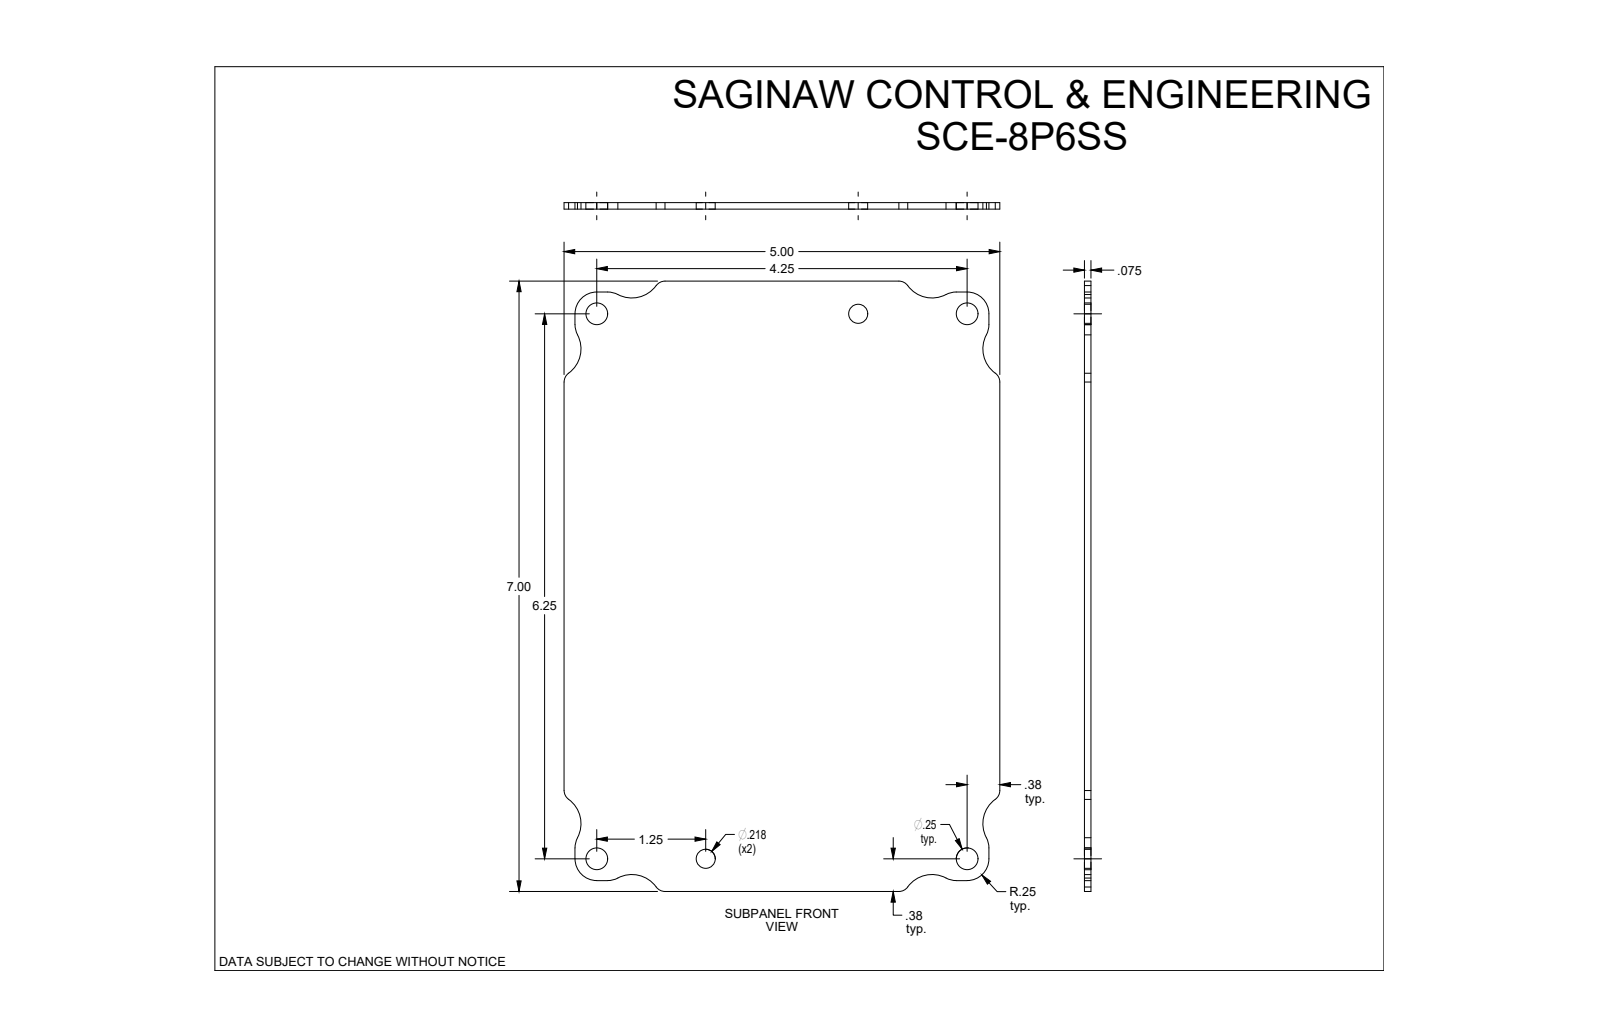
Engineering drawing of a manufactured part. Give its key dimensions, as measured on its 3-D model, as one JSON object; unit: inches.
{"part_name": "SCE-8P6SS", "step_written_by": "SolidWorks 2019 (CONFIG_CONTROL_DESIGN)", "units": "inches", "bodies": {"solids": 1, "faces": 48, "planar": 14, "cylindrical": 34, "other": 0}, "overall_size": [7, 5, 0.075], "volume_in3": 2.515, "surface_area_in2": 69.13, "round_holes": [[0.25, 4], [0.218, 2]], "partial_cylinders_radius": [[0.25, 12], [0.125, 8], [0.344, 8]], "face_to_face_distances": [0.075, 5, 7, 0.125, 4.875, 6.875, 4.75, 6.75], "hole_center_spacings": [1.25, 3, 4.25, 6.25, 6.374, 6.933, 7.558, 6.491]}
